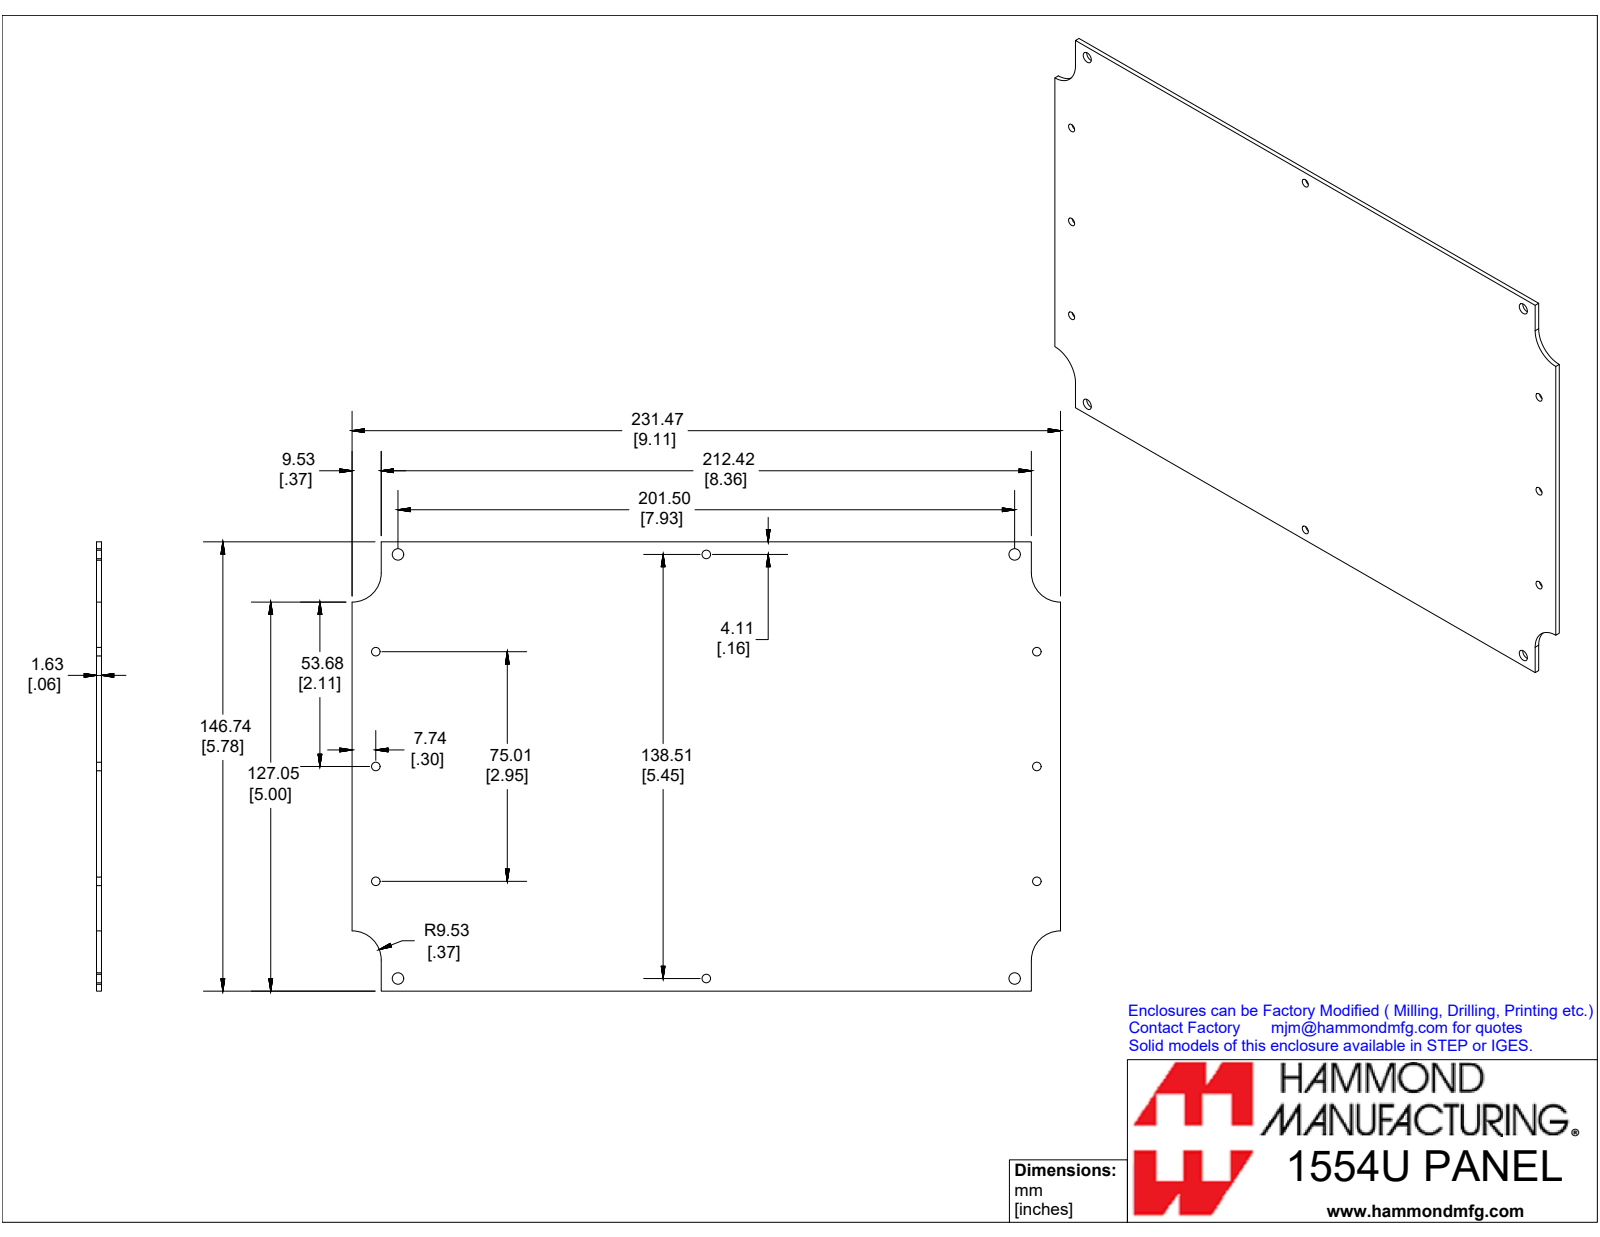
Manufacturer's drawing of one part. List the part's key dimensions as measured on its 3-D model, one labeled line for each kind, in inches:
Part name (STEP PRODUCT): 1554VPL
STEP written by: SolidWorks 2019 (CONFIG_CONTROL_DESIGN)
Units: inches
Bodies: 1 solid, 26 faces (10 planar, 16 cylindrical, 0 other)
Overall size (bounding box): 9.113 × 5.777 × 0.064
Volume: 3.293 in³ · Surface area: 105.1 in²
Round holes (diameter × count): ⌀0.11 ×8, ⌀0.147 ×4
Partial cylindrical surfaces — rounded edges, fillets, slot ends (radius × count): R0.375 ×4
Main face-to-face distances: 0.064, 5.777, 9.113, 0.375, 8.738, 8.363
Hole centre spacings: 1.282, 1.476, 2.741, 3.967, 4.213, 4.432, 5.051, 5.978
